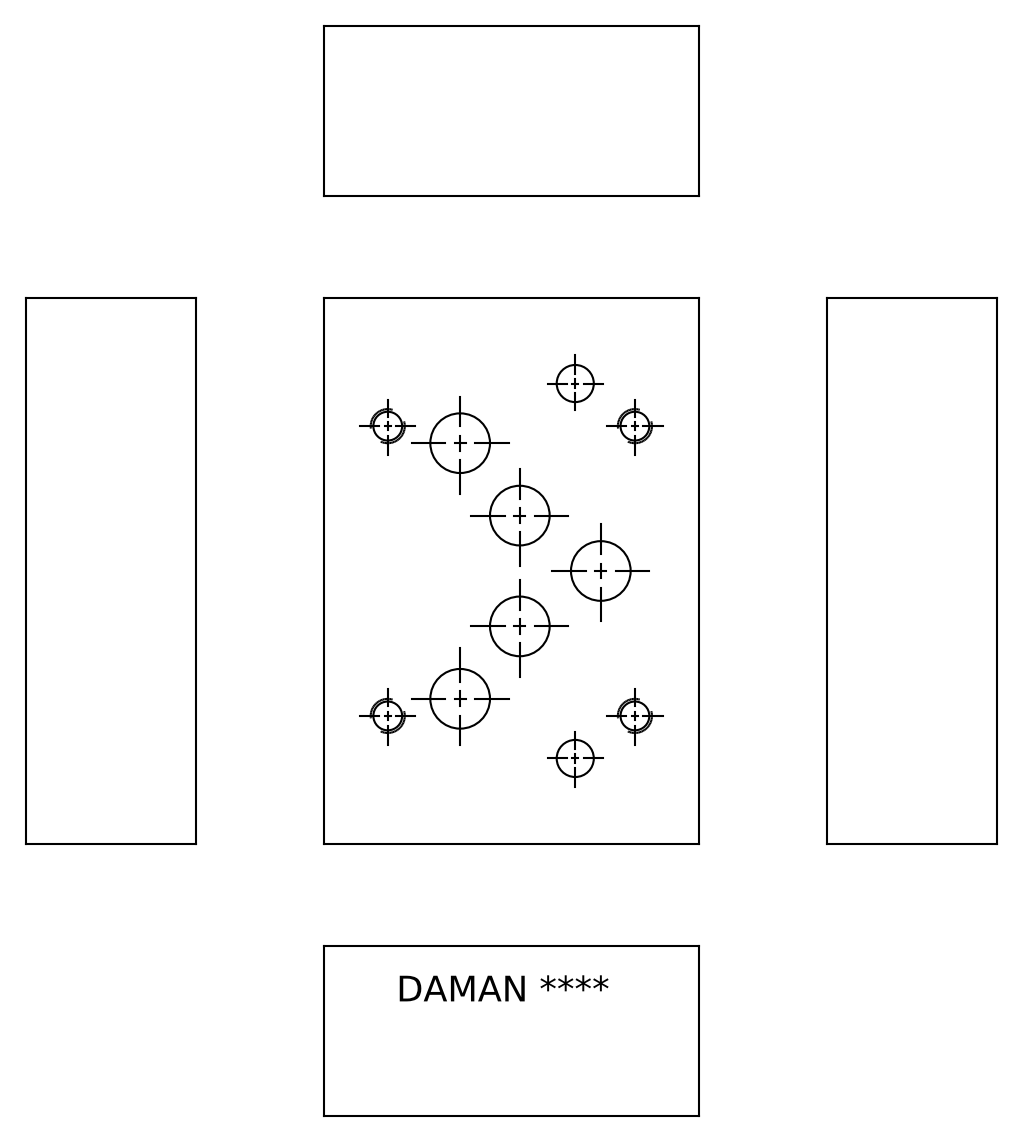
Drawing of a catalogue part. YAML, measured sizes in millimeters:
part_name: "Part_AD05HED05HVAAB.C01590R4_3D"
step_written_by: "Autodesk Inventor 2019 (AUTOMOTIVE_DESIGN)"
units: millimeters
bodies: {solids: 1, faces: 426, planar: 287, cylindrical: 29, other: 110}
overall_size: [101.6, 69.85, 31.75]
volume: 220178
surface_area: 27331
round_holes:
  - {diameter: 7.14, count: 7}
  - {diameter: 9.53, count: 6}
  - {diameter: 11.13, count: 6}
  - {diameter: 15.88, count: 5}
  - {diameter: 4.78, count: 4}
face_to_face_distances: [31.75, 69.85, 101.6, 1.02, 30.73, 68.85, 1, 19.95, 3.62, 12.87]
hole_center_spacings: [33.68, 44.71, 17.48, 20.65, 27.14, 27.15, 32.7, 38.3]
